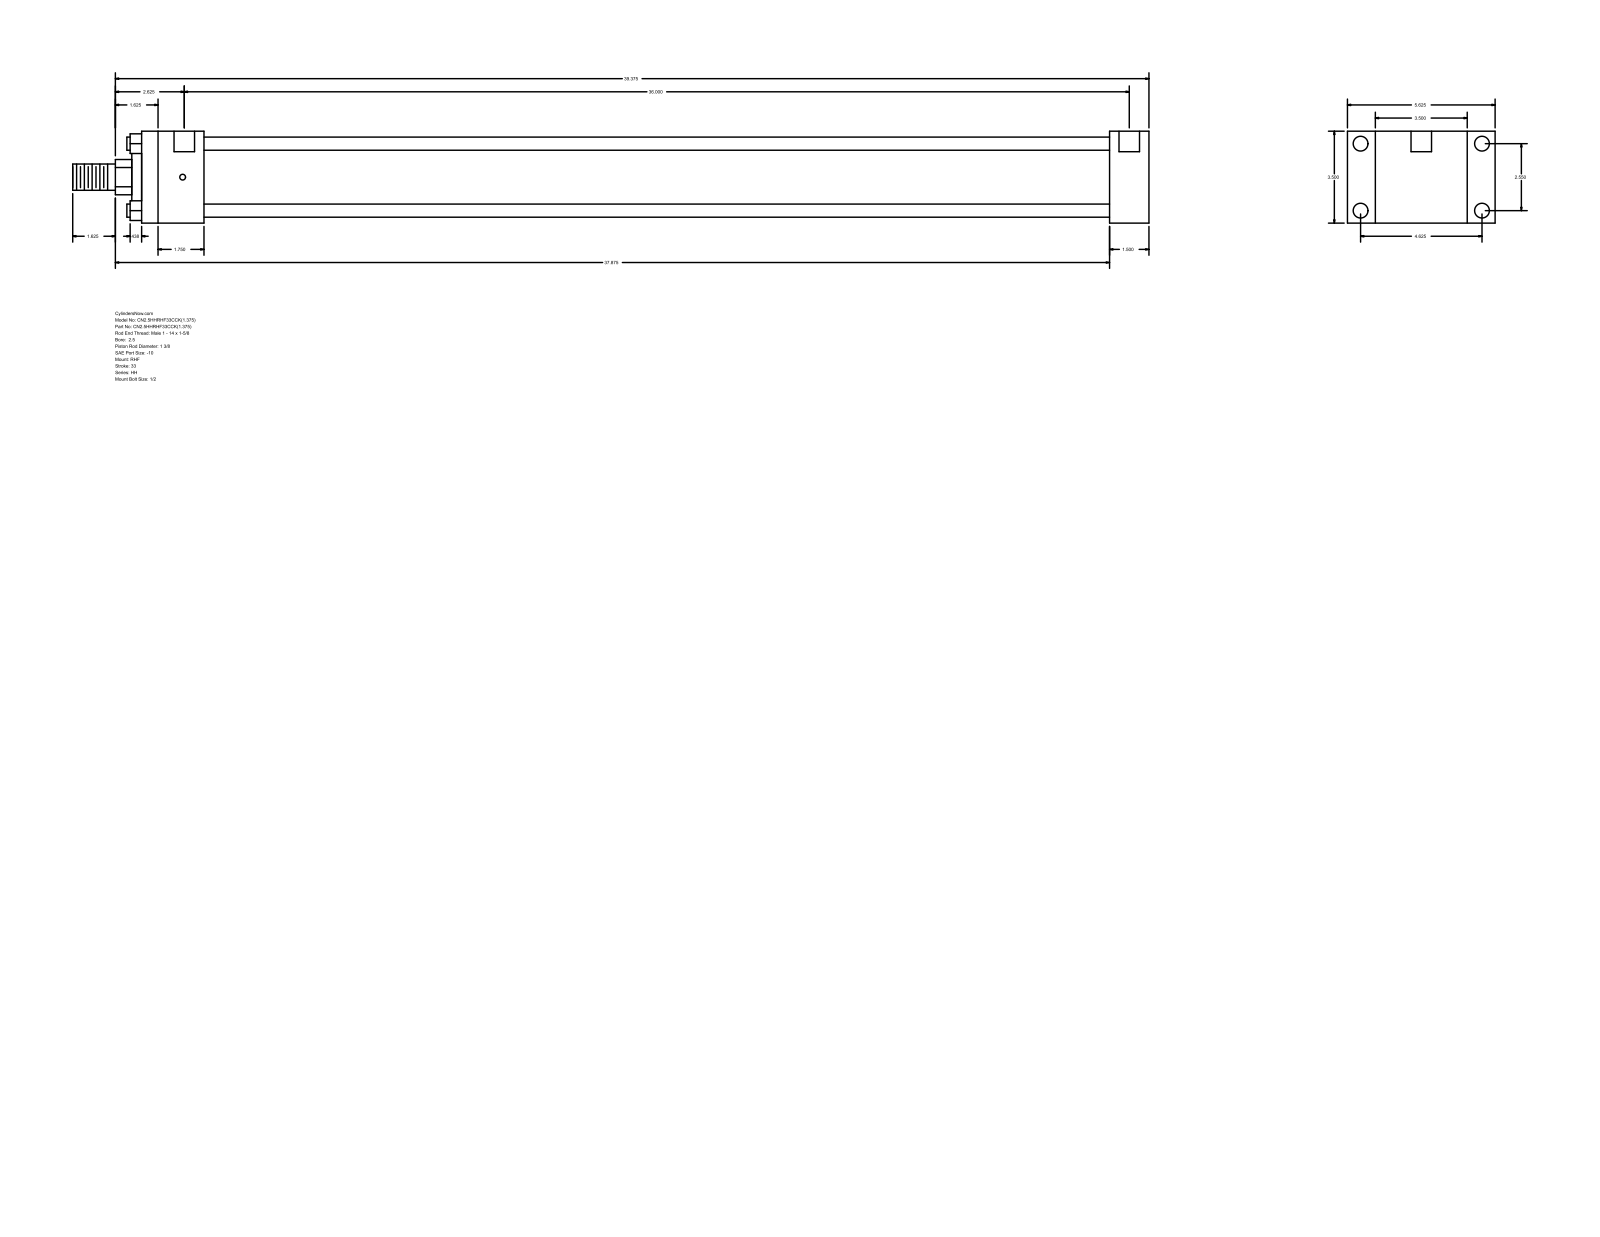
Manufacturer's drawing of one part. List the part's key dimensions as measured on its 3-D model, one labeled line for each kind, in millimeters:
Part name (STEP PRODUCT): HH_RHF__0250_1.375
STEP written by: GSSL Pune (CONFIG_CONTROL_DESIGN)
Units: millimetres
Bodies: 0 solids, 88 faces (60 planar, 28 cylindrical, 0 other)
Overall size (bounding box): 1041.4 × 142.88 × 88.9
Round holes (diameter × count): ⌀5.56 ×4, ⌀14.3 ×4, ⌀19.84 ×2
Round bosses / shafts (diameter × count): ⌀12.7 ×4, ⌀73.03 ×1, ⌀50.8 ×1, ⌀34.92 ×1, ⌀25.4 ×1
Partial cylindrical surfaces — rounded edges, fillets, slot ends (radius × count): R17.06 ×1
Main face-to-face distances: 88.9, 38.1, 26.99, 115.89, 936.62, 974.72, 142.88, 60.32, 876.3, 914.4
Hole centre spacings: 1.58, 64.76, 117.48, 134.15, 915.99, 917.57, 914.41
